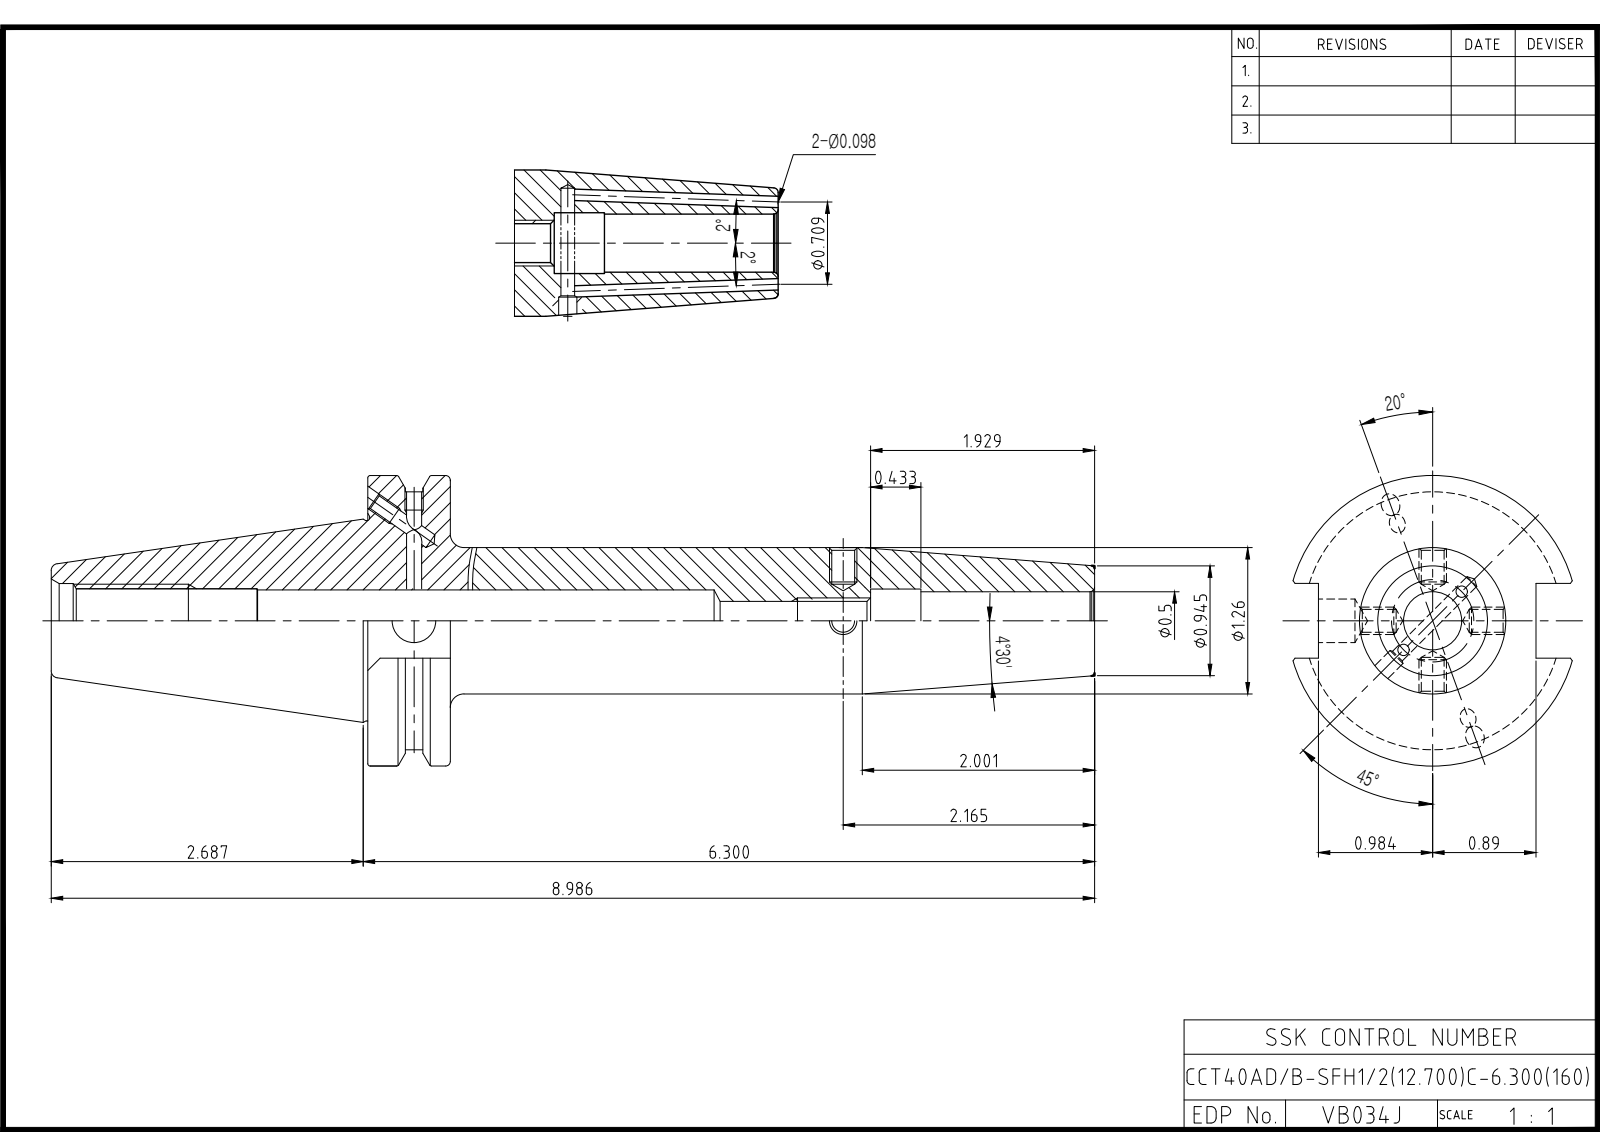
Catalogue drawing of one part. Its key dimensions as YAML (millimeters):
part_name: "LO-CCT40ADB-SFH5_8C-3_15"
step_written_by: "CREO PARAMETRIC BY PTC INC, 2018100 (CONFIG_CONTROL_DESIGN)"
units: millimeters
bodies: {solids: 1, faces: 143, planar: 47, cylindrical: 62, other: 34}
overall_size: [148.25, 63.5, 61]
volume: 139328
surface_area: 31637
round_holes:
  - {diameter: 4, count: 7}
  - {diameter: 3.4, count: 3}
  - {diameter: 9.53, count: 1}
  - {diameter: 11, count: 1}
  - {diameter: 12, count: 1}
  - {diameter: 13.5, count: 1}
  - {diameter: 14, count: 1}
  - {diameter: 15.88, count: 1}
  - {diameter: 16.3, count: 1}
  - {diameter: 16.48, count: 1}
round_bosses_or_shafts:
  - {diameter: 63.5, count: 1}
  - {diameter: 43.8, count: 1}
  - {diameter: 34, count: 1}
partial_cylinders:
  - {radius: 28.15, count: 1}
face_to_face_distances: [18.05, 79, 60.95, 47.6, 69.25, 87.3, 148.25, 16.38, 96.25, 27]
